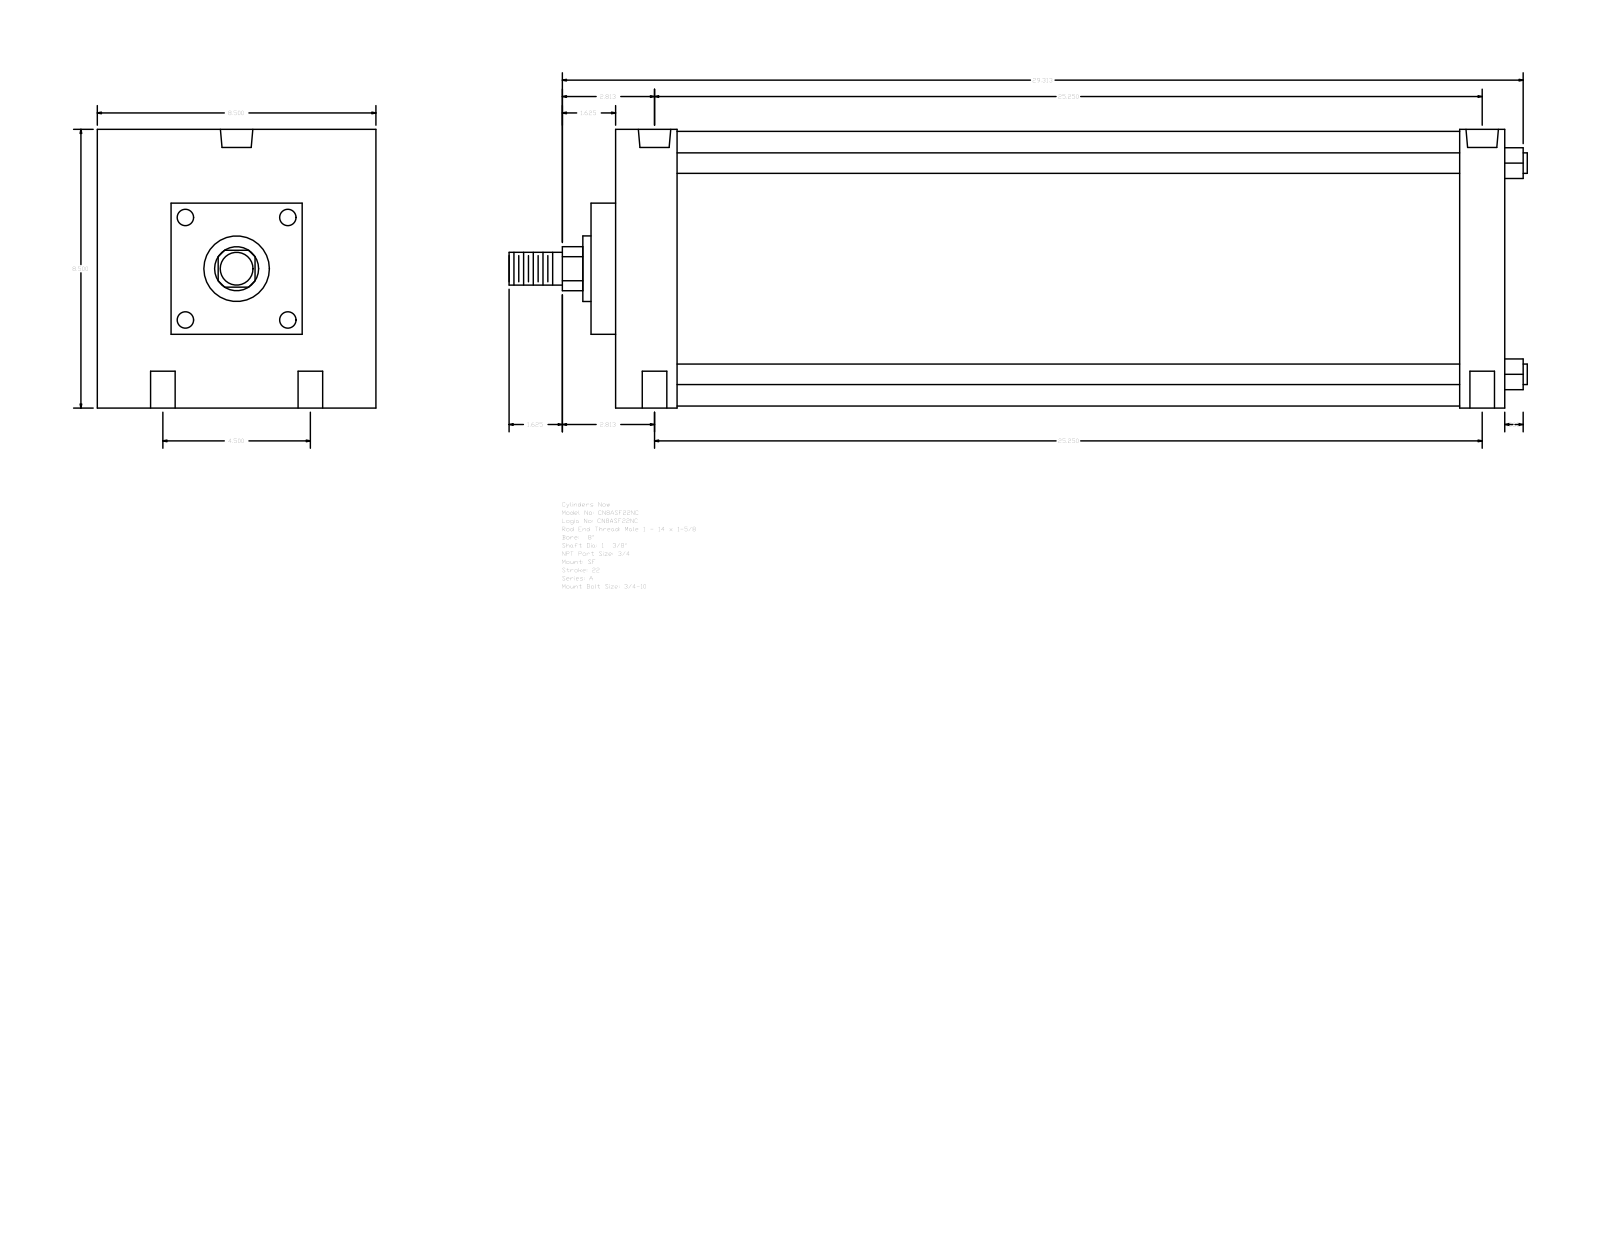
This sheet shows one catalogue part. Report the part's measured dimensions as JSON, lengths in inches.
{"part_name": "A_SF__0800_1.375", "step_written_by": "GSSL Pune (CONFIG_CONTROL_DESIGN)", "units": "inches", "bodies": {"solids": 0, "faces": 93, "planar": 67, "cylindrical": 26, "other": 0}, "overall_size": [31.063, 8.5, 8.5], "round_holes": [[0.75, 4], [0.594, 2], [0.989, 2]], "round_bosses_or_shafts": [[0.625, 4], [8.375, 1], [2, 1], [1.375, 1], [1, 1]], "partial_cylinders_radius": [[0.672, 1]], "face_to_face_distances": [27.125, 8.5, 1.875, 25.75, 23.875, 25.25, 1.375, 0.75, 2.625, 26.5], "hole_center_spacings": [2.25, 25.35, 25.25, 4.5, 25.648, 24.75]}
